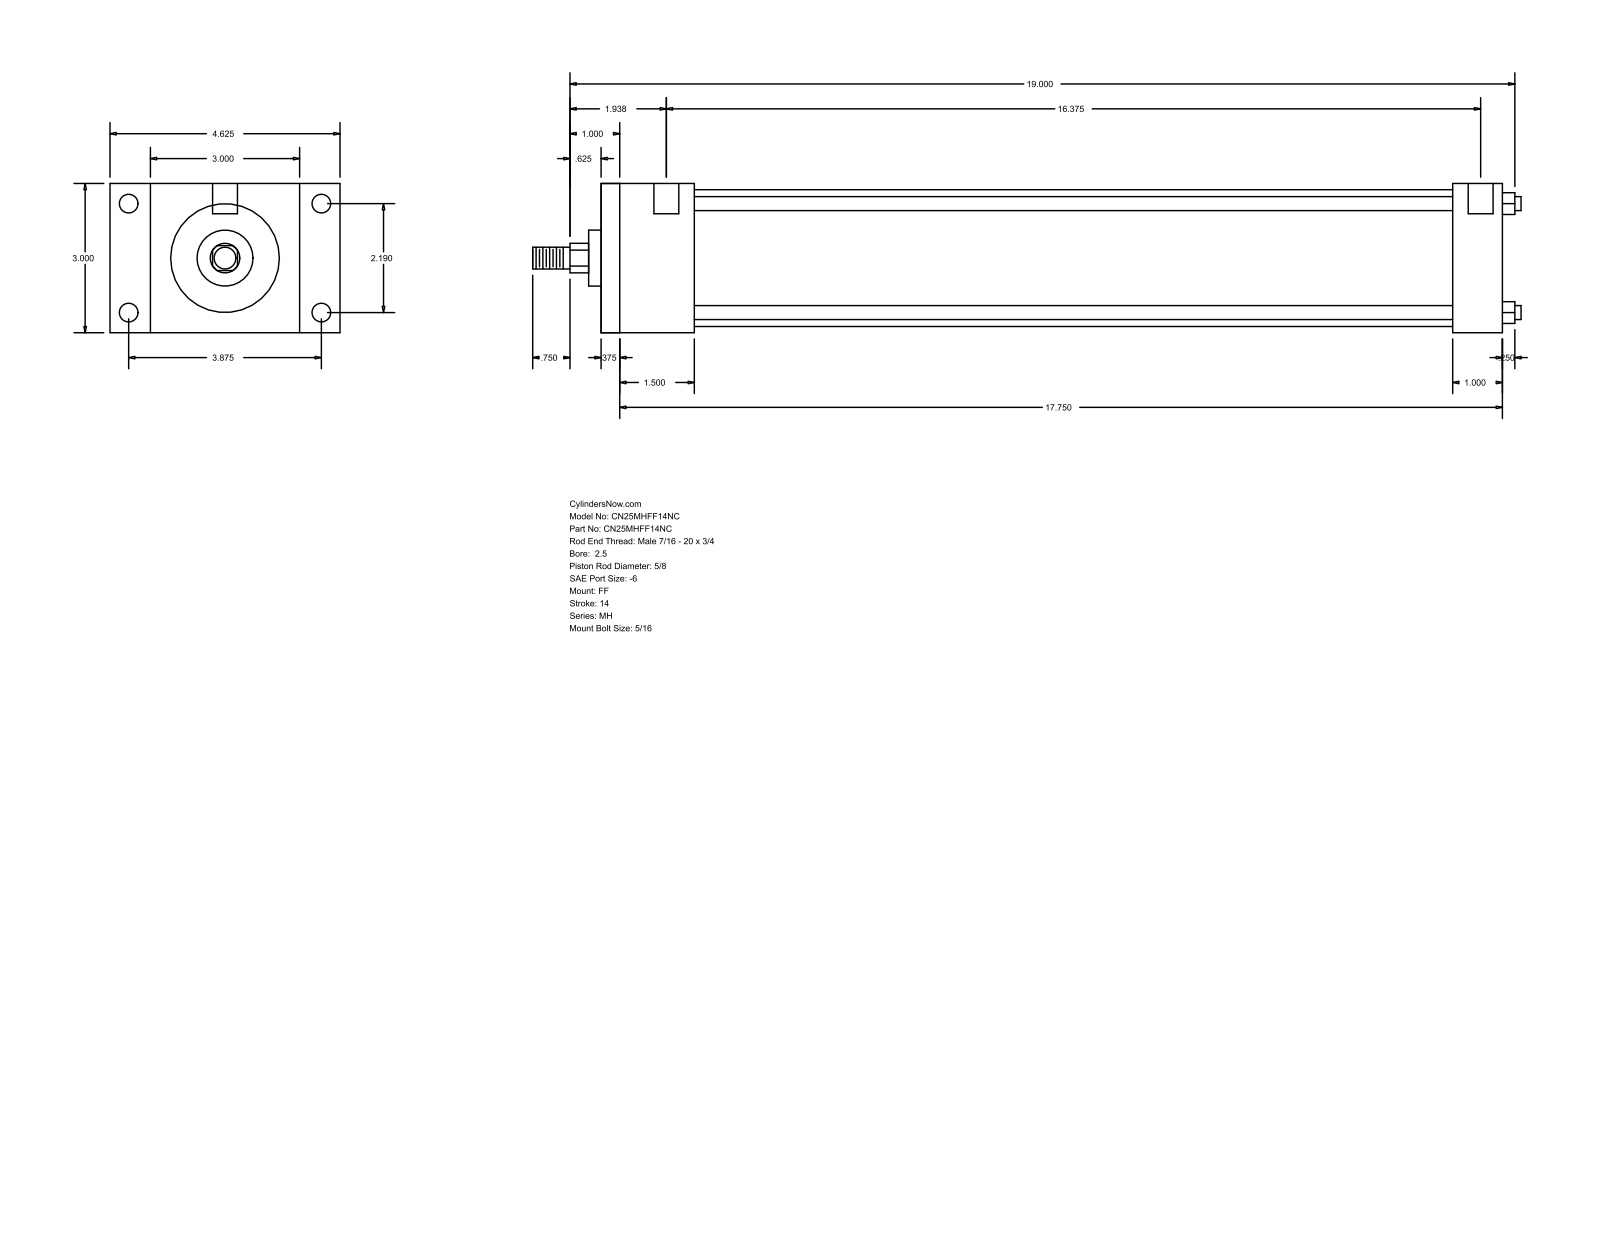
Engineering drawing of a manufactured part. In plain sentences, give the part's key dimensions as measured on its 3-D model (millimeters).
The part is named "MH_FF__0250_0.625". Its 3-D file was written by "GSSL Pune (CONFIG_CONTROL_DESIGN)". It is 0 solids with 92 faces: 64 planar, 28 cylindrical and 0 other. Overall it measures 504.82 by 117.47 by 76.2 millimeters. Round holes: 4 of diameter 5.56, 4 of diameter 9.53, 2 of diameter 12.7. Round bosses or shafts: 4 of diameter 7.14, 1 of diameter 69.85, 1 of diameter 28.57, 1 of diameter 15.88, 1 of diameter 11.11. Partial cylindrical surfaces (rounded edges, fillets, slot ends): 1 of radius 7.54. The main face-to-face distances are 76.2, 460.37, 9.52, 450.85, 25.4, 47.62, 434.97, 38.1, 425.45, 387.35. The hole center spacings are 55.62, 98.42, 113.05, 423.86, 3.17, 4.76, 415.93, 419.1.
